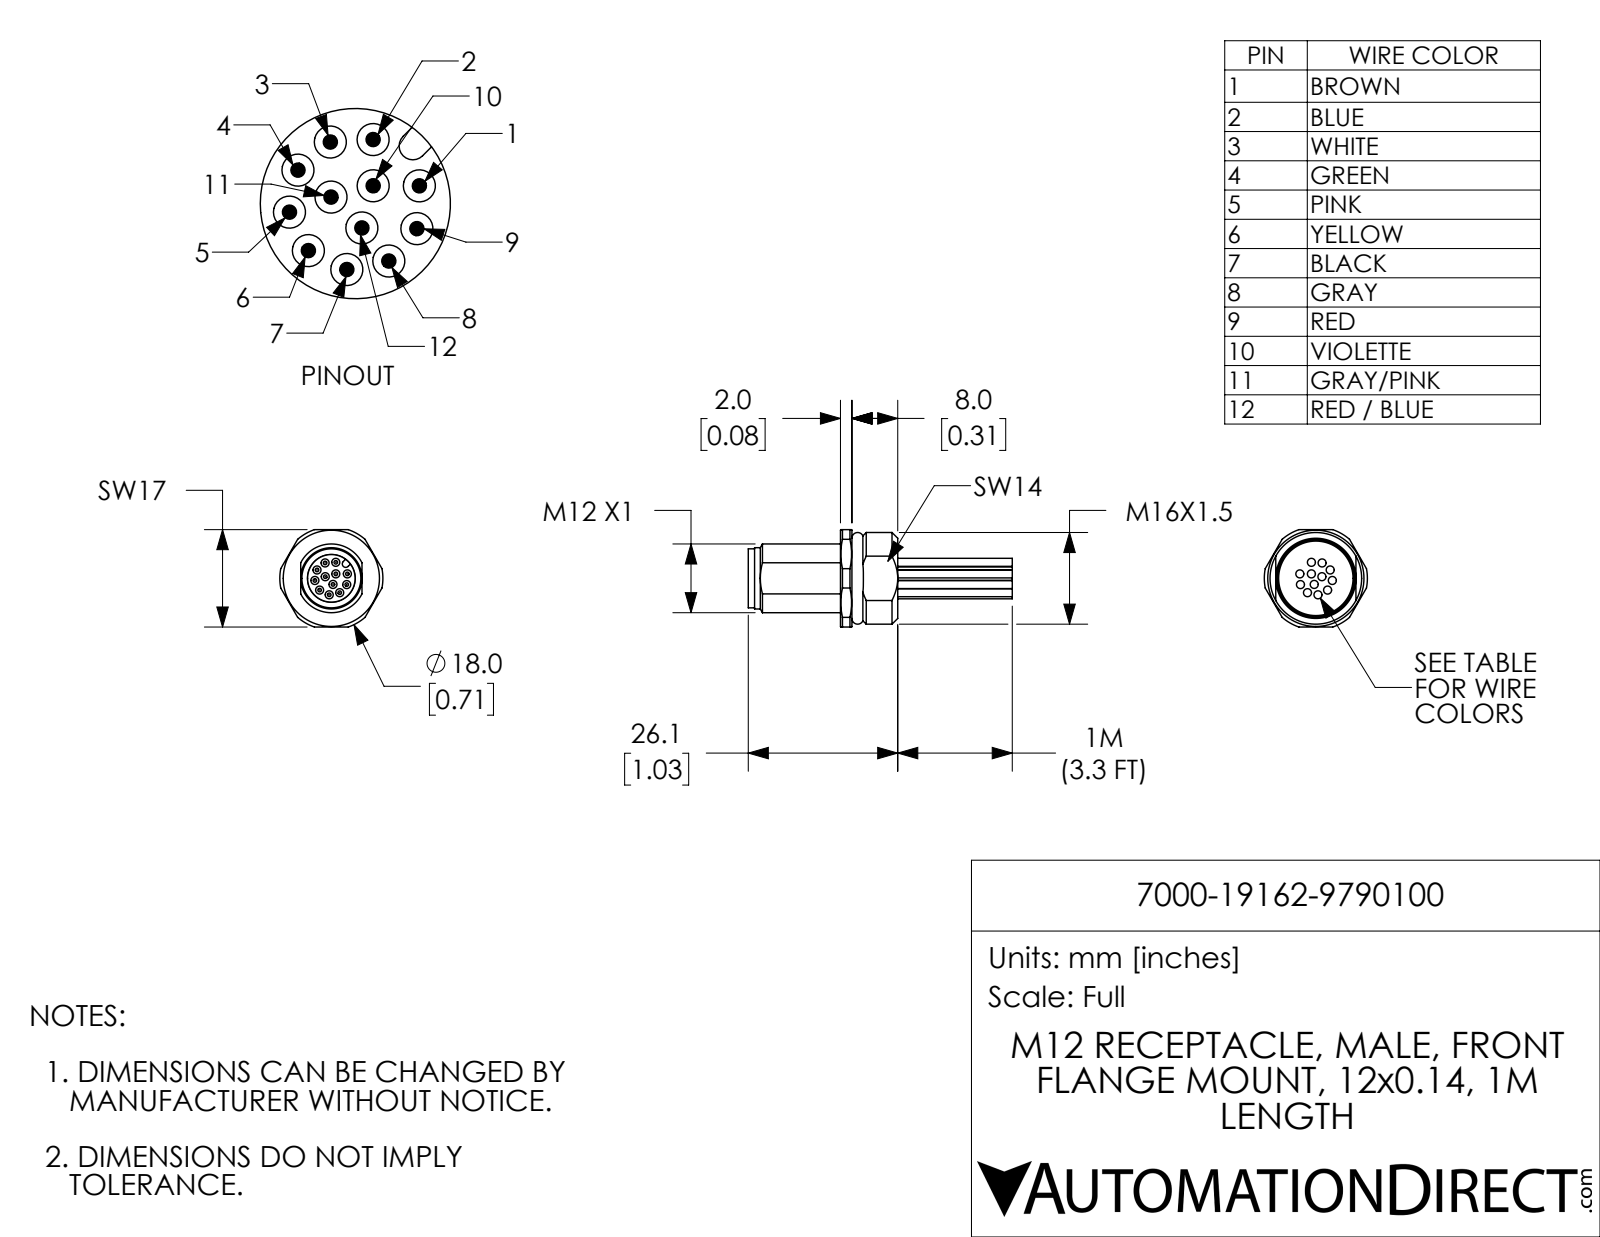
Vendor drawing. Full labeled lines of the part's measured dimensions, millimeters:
Part name (STEP PRODUCT): 7000-19162-9790100
STEP written by: SolidWorks 2017 (AUTOMOTIVE_DESIGN)
Units: millimetres
Bodies: 1 solid, 188 faces (56 planar, 92 cylindrical, 40 other)
Overall size (bounding box): 46.1 × 18 × 17
Volume: 3 470 mm³ · Surface area: 3 208 mm²
Round holes (diameter × count): ⌀1.4 ×12, ⌀8.3 ×1, ⌀13 ×1
Round bosses / shafts (diameter × count): ⌀0.6 ×12, ⌀10.7 ×1, ⌀10.3 ×1
Partial cylindrical surfaces — rounded edges, fillets, slot ends (radius × count): R0.6 ×1, R6 ×1, R8 ×1, R9 ×1
Main face-to-face distances: 9, 1.7, 12.3, 10.7, 7, 2, 14, 17, 16.2, 9.2
Hole centre spacings: 2.9, 1.9, 3.5, 4.9, 1.1, 3.6, 1.9, 1.9
